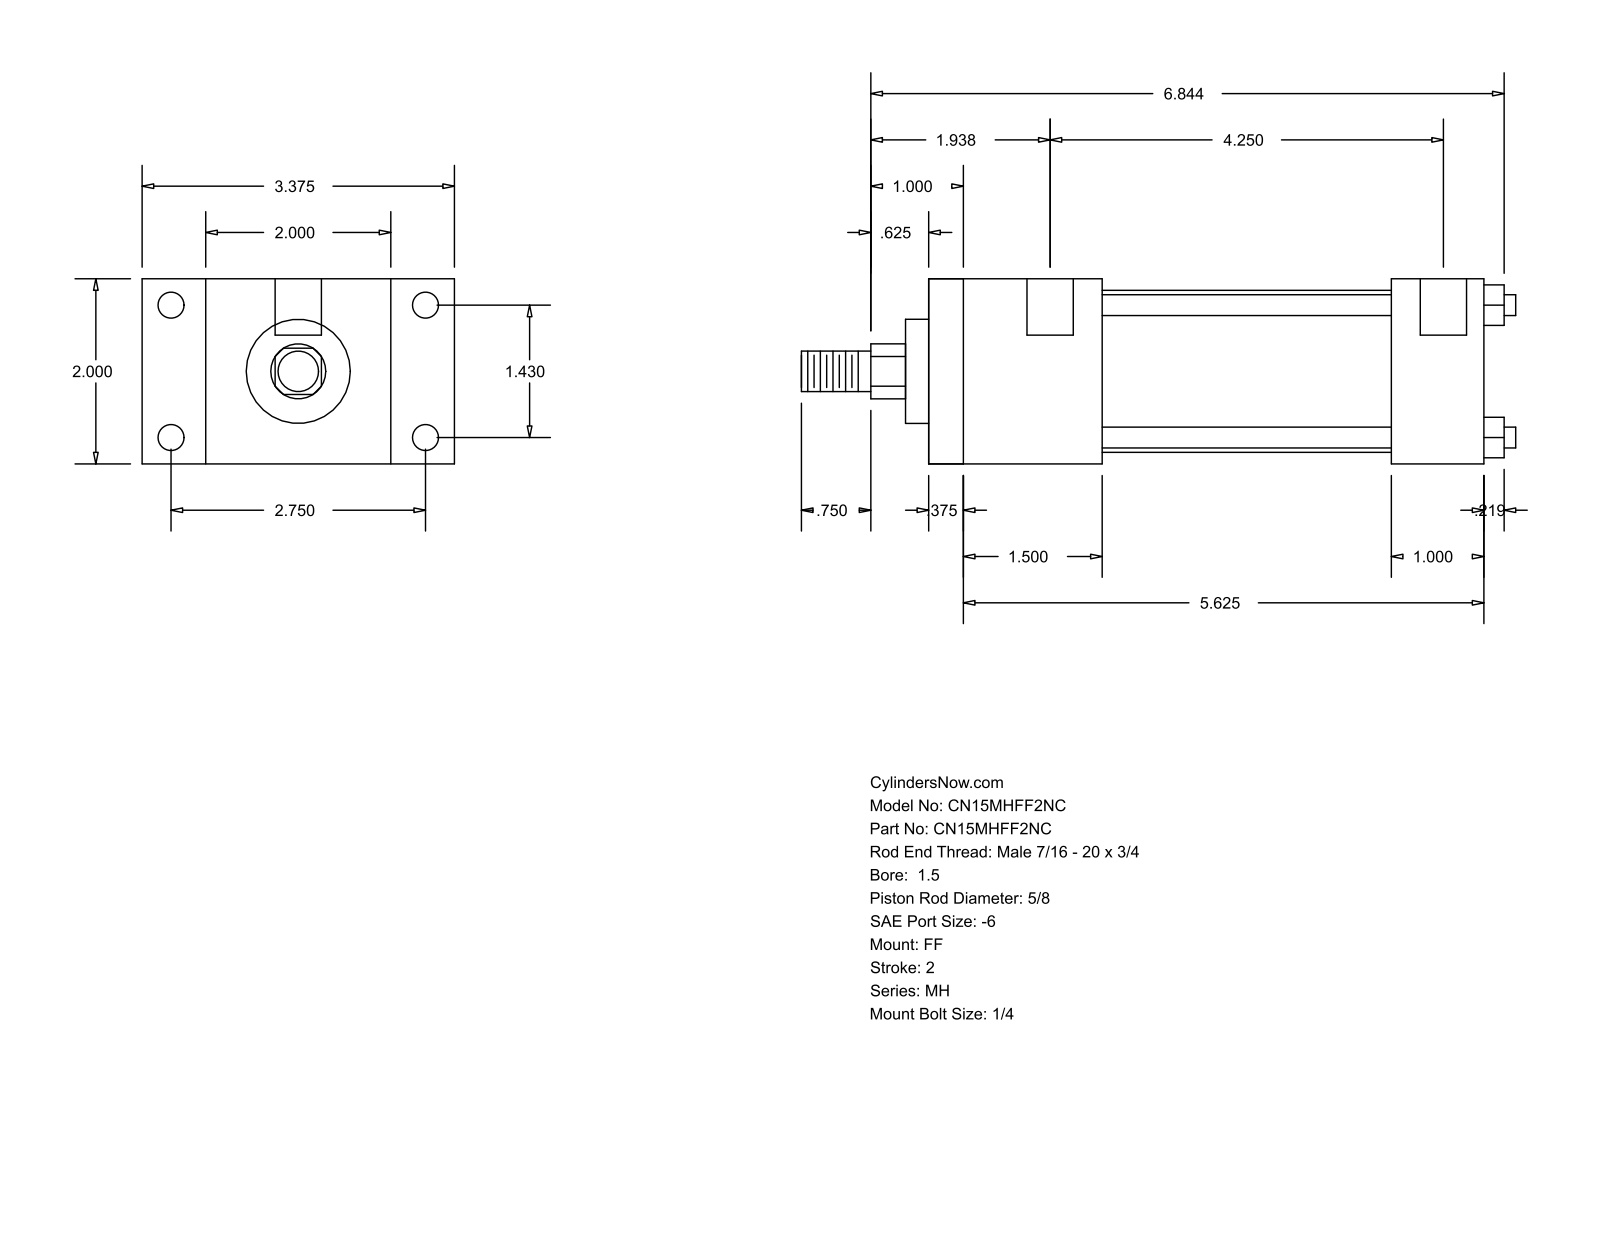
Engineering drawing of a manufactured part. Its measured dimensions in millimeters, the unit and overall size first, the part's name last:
Units: millimetres
Overall size (bounding box): 196.06 × 85.72 × 50.8
Round holes (diameter × count): ⌀5.56 ×4, ⌀7.14 ×4, ⌀12.7 ×2
Round bosses / shafts (diameter × count): ⌀5.71 ×4, ⌀44.45 ×1, ⌀28.57 ×1, ⌀15.88 ×1, ⌀11.11 ×1
Partial cylindrical surfaces — rounded edges, fillets, slot ends (radius × count): R7.54 ×1
Main face-to-face distances: 50.8, 152.4, 142.88, 9.52, 25.4, 17.46, 68.26, 47.62, 38.1, 104.78
Hole centre spacings: 36.32, 69.84, 78.72, 111.12, 3.17, 107.95
Bodies: 0 solids, 92 faces (64 planar, 28 cylindrical, 0 other)
Part name (STEP PRODUCT): MH_FF__0150_0.625
STEP written by: GSSL Pune (CONFIG_CONTROL_DESIGN)
